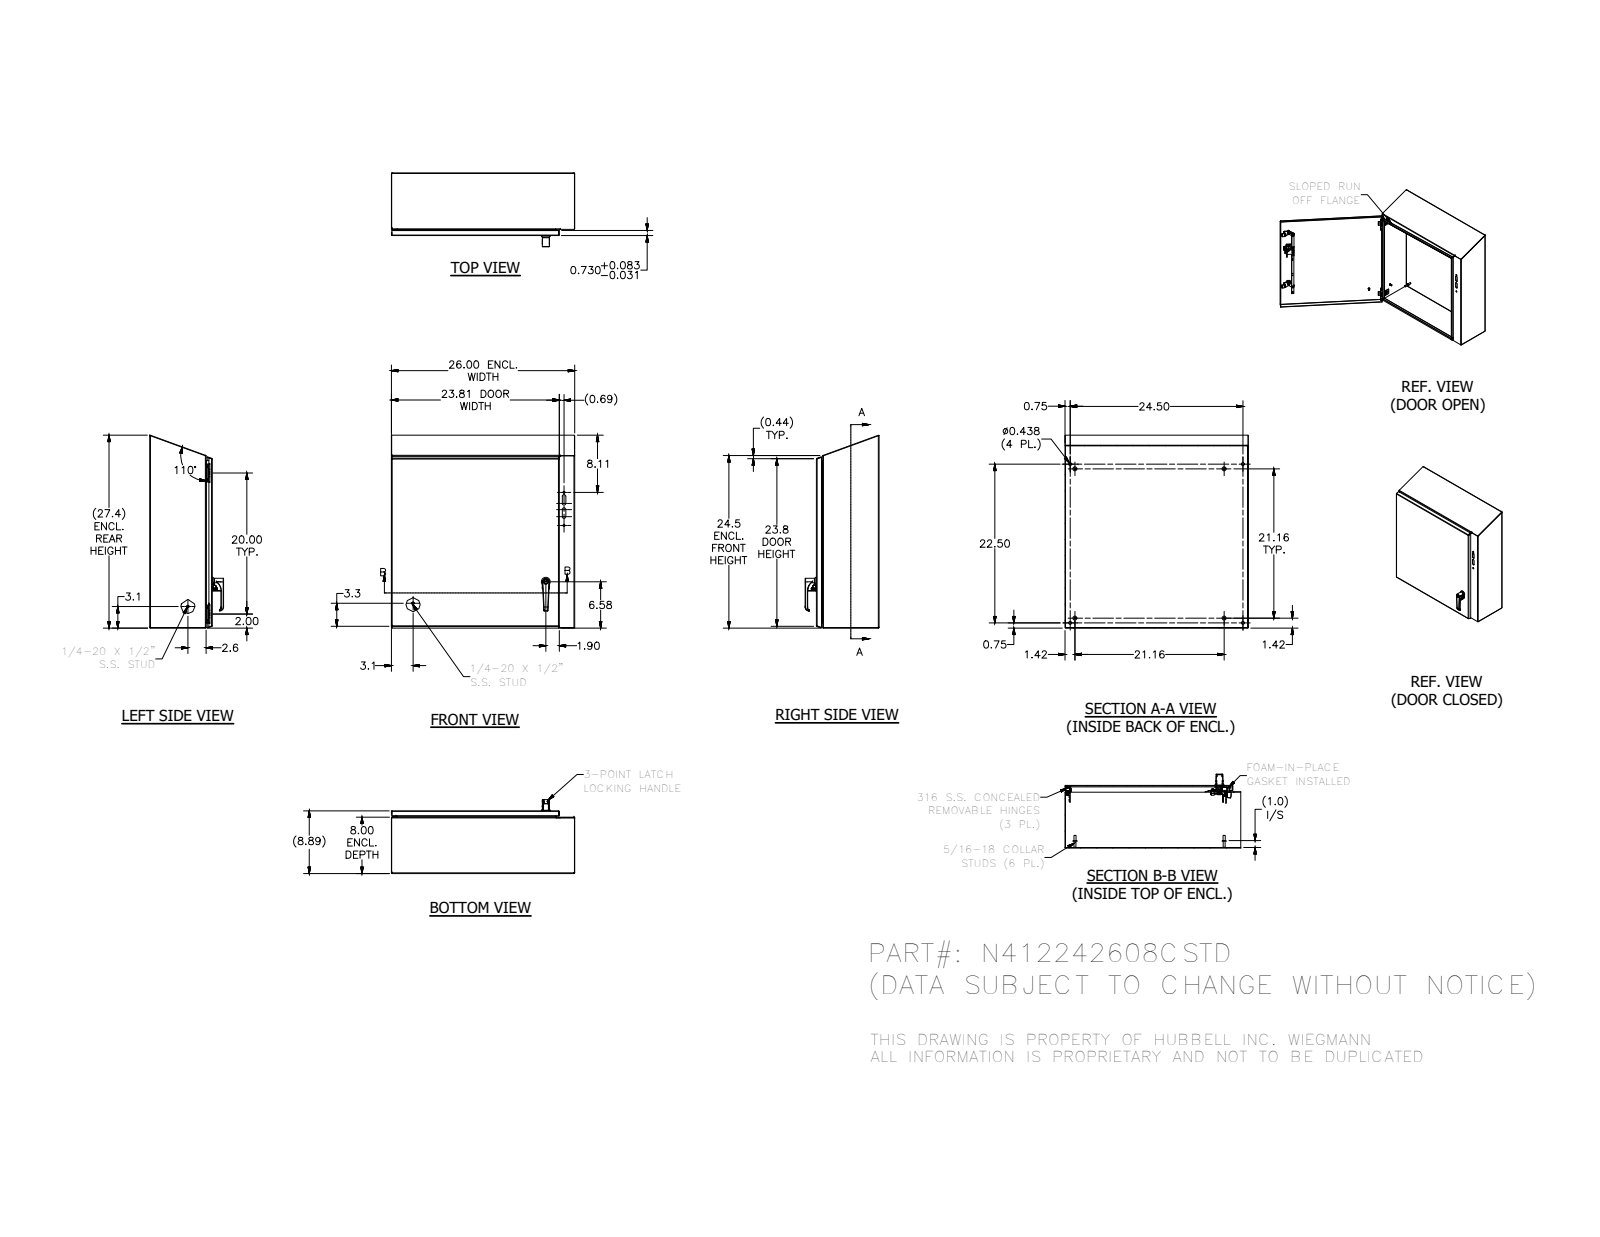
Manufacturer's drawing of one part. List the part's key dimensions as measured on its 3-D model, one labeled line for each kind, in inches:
Part name (STEP PRODUCT): N412242608CSTDB3S; 388150; N4122608CSTDTOP; 38846 (+8 more)
STEP written by: Autodesk Inventor 2014 (AUTOMOTIVE_DESIGN)
Units: inches
Bodies: 62 solids, 2137 faces (861 planar, 753 cylindrical, 523 other)
Overall size (bounding box): 27.366 × 26 × 10.481
Volume: 182.1 in³ · Surface area: 4 886 in²
Round holes (diameter × count): ⌀0.145 ×6, ⌀0.156 ×5, ⌀0.093 ×4, ⌀0.152 ×4, ⌀0.167 ×4, ⌀0.172 ×4, ⌀0.187 ×4, ⌀0.437 ×4, ⌀0.32 ×3, ⌀0.196 ×2, ⌀0.211 ×2, ⌀0.22 ×2
Round bosses / shafts (diameter × count): ⌀0.25 ×12, ⌀0.3 ×8, ⌀0.563 ×4, ⌀0.437 ×4, ⌀0.36 ×4, ⌀0.32 ×4, ⌀0.275 ×4, ⌀0.256 ×4
Partial cylindrical surfaces — rounded edges, fillets, slot ends (radius × count): R0.02 ×38, R0.012 ×31, R0.031 ×29, R0.05 ×26, R0.125 ×24, R0.105 ×19, R0.016 ×18, R0.025 ×16
Main face-to-face distances: 0.074, 8.813, 8.739, 8.887, 25.926, 7.926, 0.887, 25.852, 26, 0.813
Hole centre spacings: 20, 0.5, 14.625, 14.625, 24.9, 0.656, 0.66, 0.984
